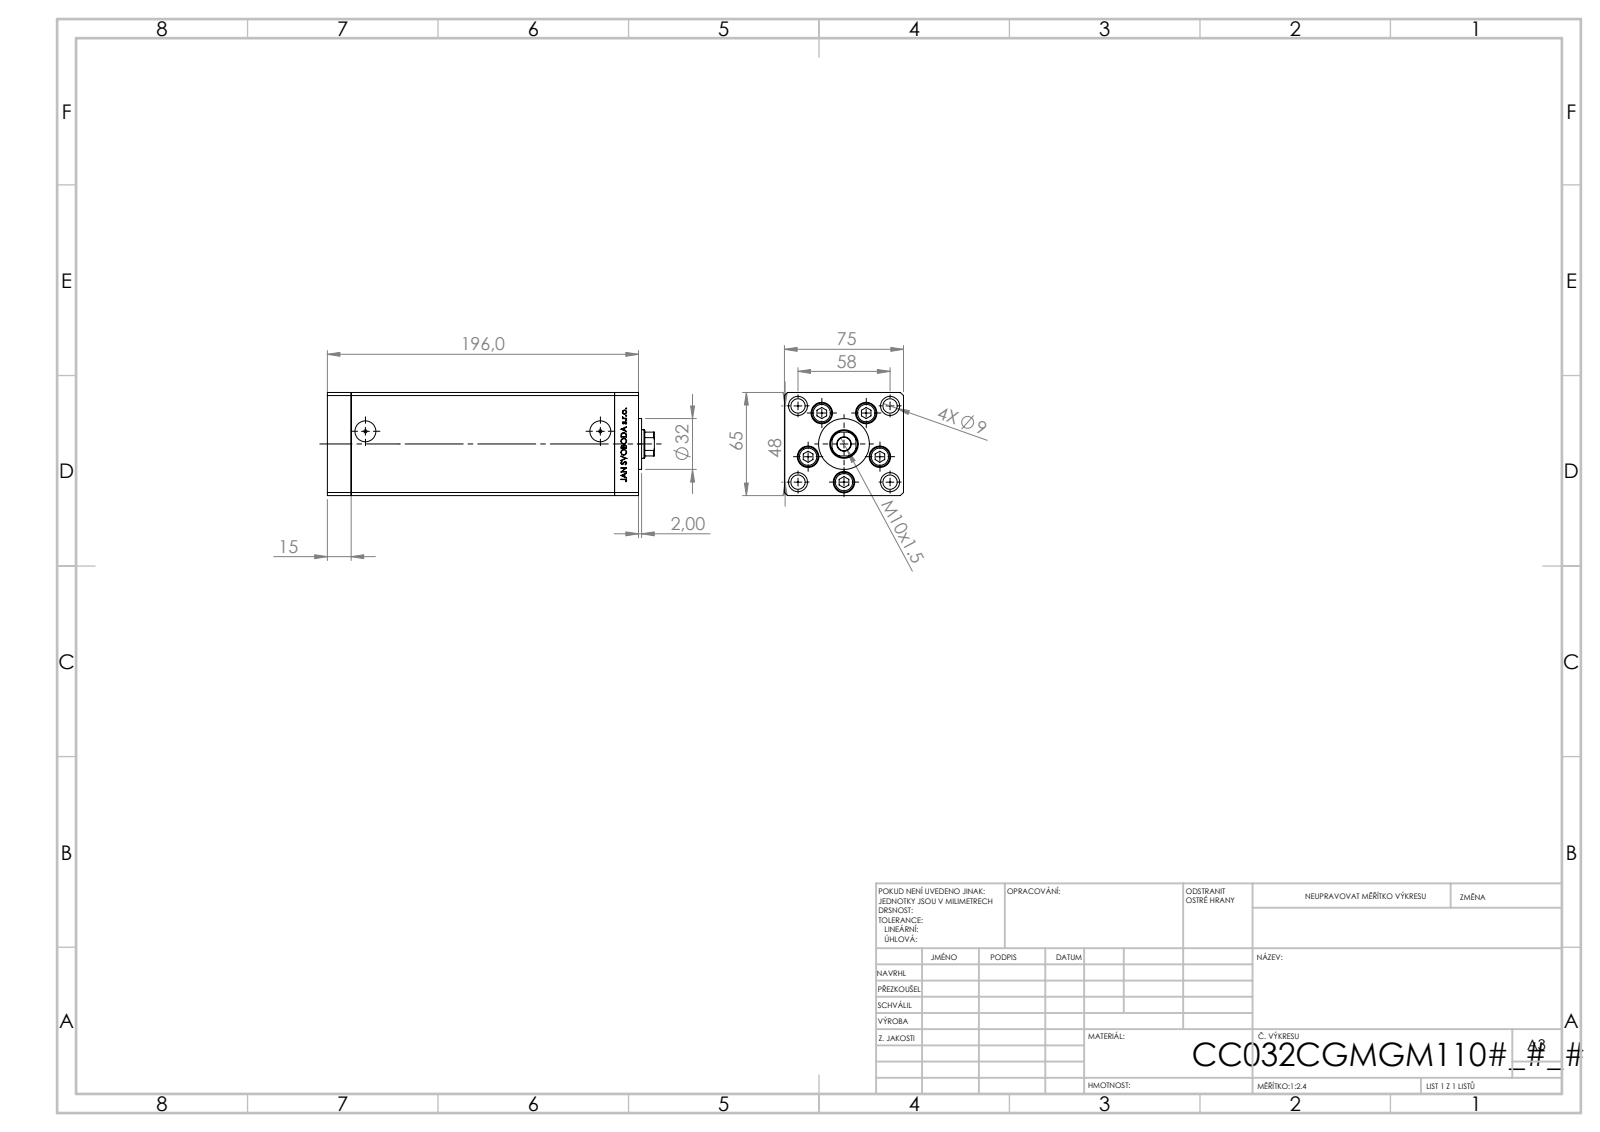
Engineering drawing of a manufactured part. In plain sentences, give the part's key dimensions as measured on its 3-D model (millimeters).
The part is named "V220C_VC_C; V220C FRONT; ALLEN BOLT; V220C_C MIDDLE (+1 more)". Its 3-D file was written by "SolidWorks 2019 (CONFIG_CONTROL_DESIGN)". It is 13 solids with 1173 faces: 544 planar, 167 cylindrical and 462 other. Overall it measures 206 by 75 by 65 millimeters. Its volume is 797 094 cubic millimeters and its surface area 159 893 square millimeters. Round holes: 9 of diameter 9, 5 of diameter 13.5, 4 of diameter 8, 4 of diameter 12, 2 of diameter 2, 2 of diameter 13.16, 1 of diameter 8.5, 1 of diameter 12.5, 1 of diameter 18. Round bosses or shafts: 5 of diameter 8, 4 of diameter 12.5, 1 of diameter 32. Partial cylindrical surfaces (rounded edges, fillets, slot ends): 2 of radius 0.93, 1 of radius 8.5. The main face-to-face distances are 75, 65, 15, 166, 181, 196, 54.5, 10.5, 28, 26.25. The hole center spacings are 24, 37.64, 15.67, 17.22, 27.71, 28.83, 29, 32.63.
